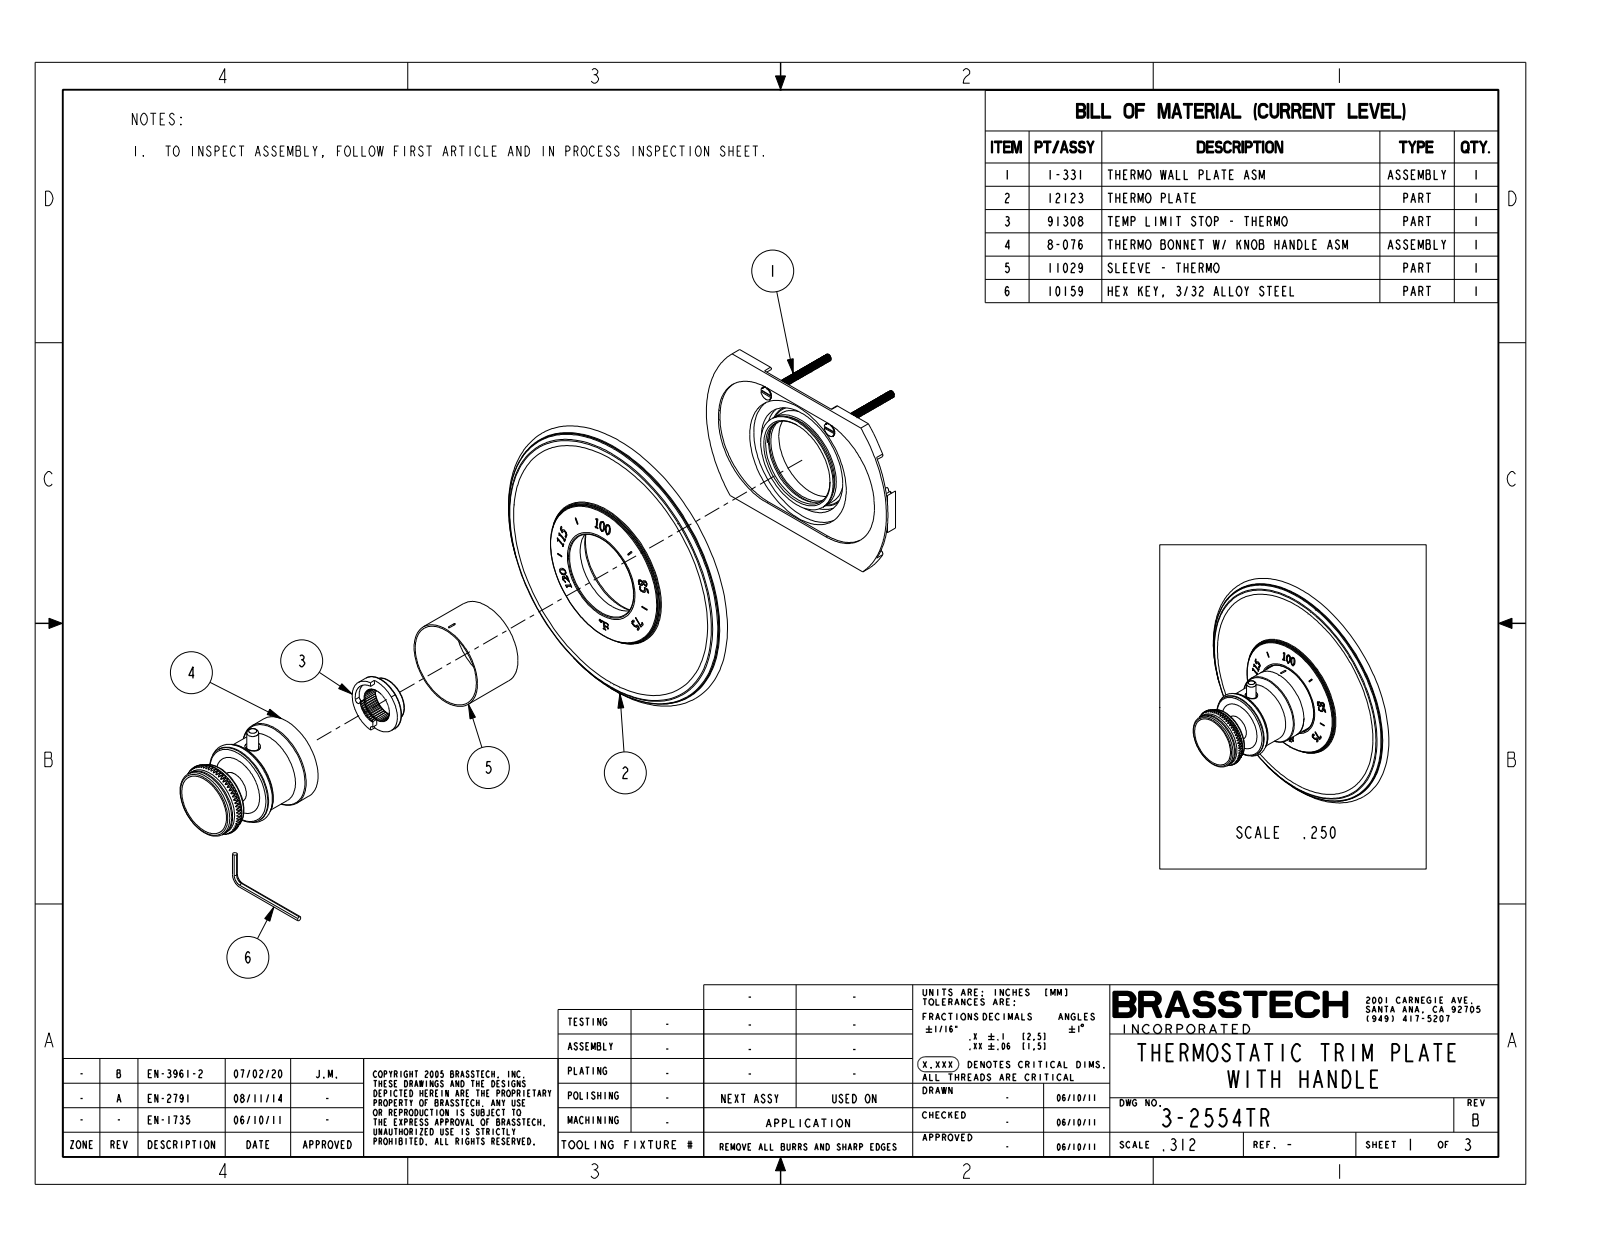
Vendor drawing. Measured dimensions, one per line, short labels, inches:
name: 3-2544TR
written by: CREO PARAMETRIC BY PTC INC, 2018400 (CONFIG_CONTROL_DESIGN)
unit: in
bodies: 1 solid, 102 faces (13 planar, 20 cylindrical, 69 other)
size: 6.75 × 6.75 × 3.581
volume: 18.7 in³; area: 93.06 in²
bosses: 1× ⌀6.53, 1× ⌀3.325, 1× ⌀1.97, 1× ⌀1.8, 1× ⌀1.66, 1× ⌀1.53, 1× ⌀0.26
face distances: 0.263, 2.422, 2.159, 2.982, 2.719, 0.56, 2.202, 1.939, 0.22, 0.78
